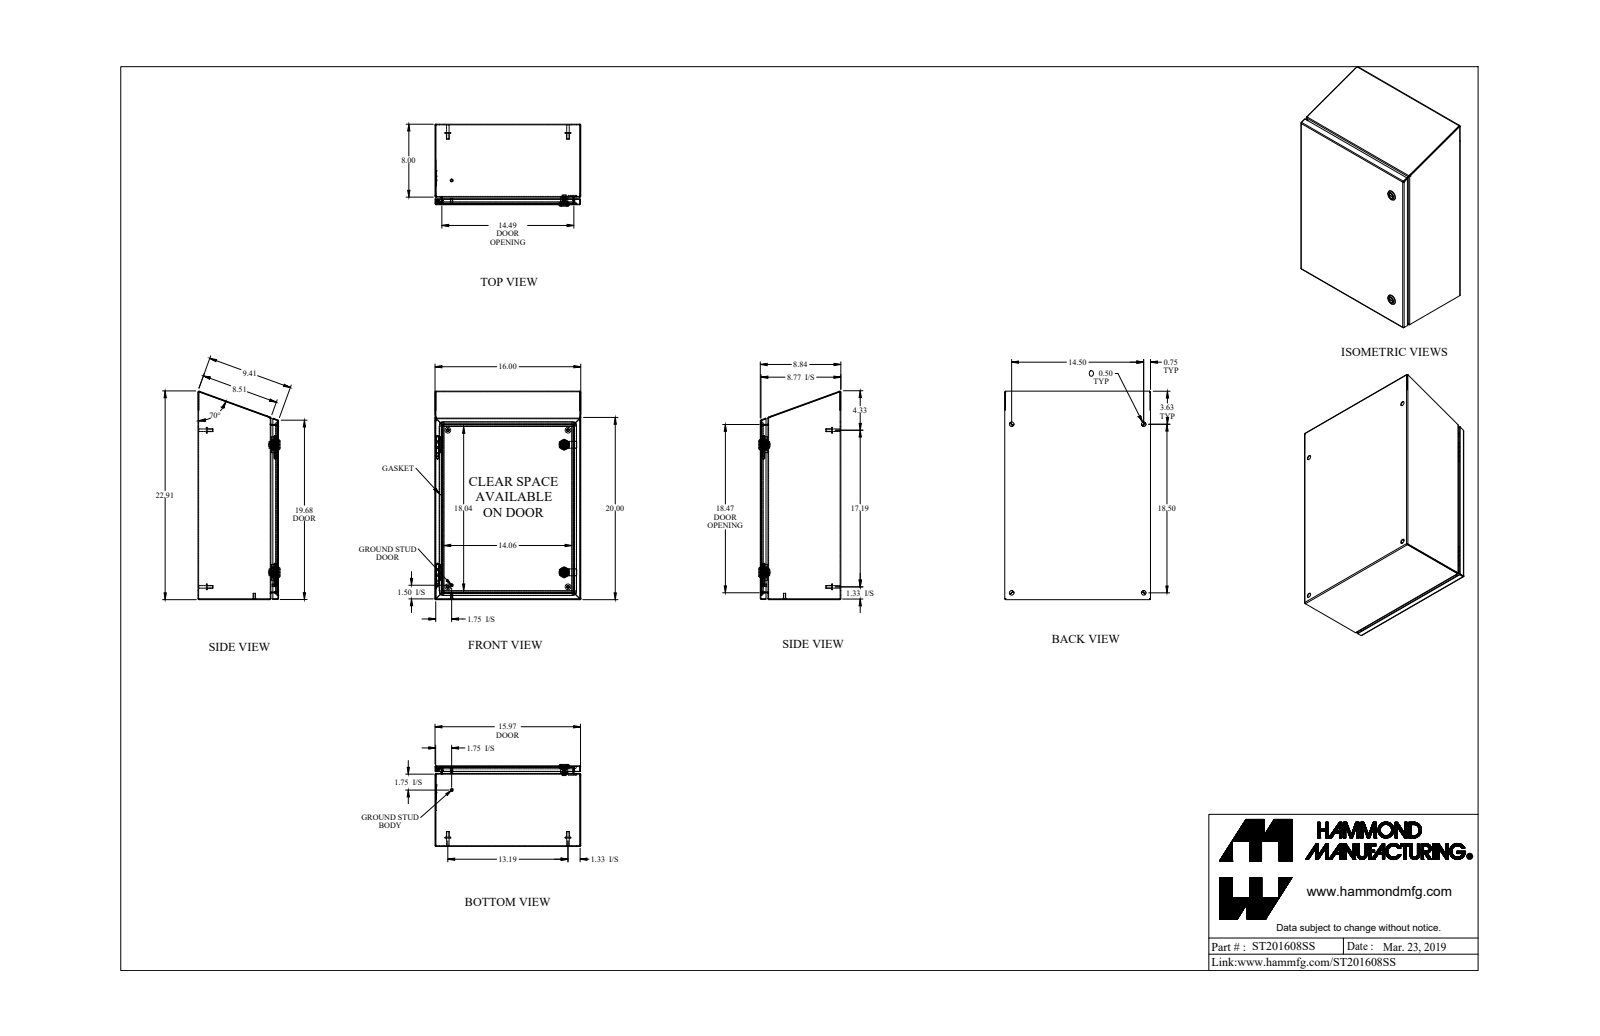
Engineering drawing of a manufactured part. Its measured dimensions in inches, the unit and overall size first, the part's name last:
Units: inches
Overall size (bounding box): 22.883 × 16 × 8.997
Round holes (diameter × count): ⌀0.5 ×6, ⌀0.197 ×2, ⌀0.387 ×2, ⌀0.63 ×2, ⌀0.768 ×2, ⌀0.172 ×1, ⌀0.24 ×1, ⌀0.242 ×1
Round bosses / shafts (diameter × count): ⌀0.625 ×6, ⌀0.313 ×6, ⌀0.275 ×4, ⌀1.1 ×2, ⌀0.785 ×2, ⌀0.525 ×2, ⌀0.25 ×2, ⌀0.236 ×2
Partial cylindrical surfaces — rounded edges, fillets, slot ends (radius × count): R0.036 ×20, R0.108 ×20, R0.25 ×11, R0.006 ×4, R0.062 ×4, R0.125 ×4, R0.499 ×4, R0.307 ×2
Main face-to-face distances: 0.072, 8.765, 8.693, 15.928, 8.837, 15.856, 16, 7.928, 0.837, 0.909
Hole centre spacings: 2.493, 13.613, 14.5, 16.285, 18.5, 21.079, 23.506, 14
Volume: 110.2 in³ · Surface area: 3 031 in²
Bodies: 27 solids, 776 faces (410 planar, 230 cylindrical, 136 other)
Part name (STEP PRODUCT): ST201608SS
STEP written by: SolidWorks 2018 (AUTOMOTIVE_DESIGN)
